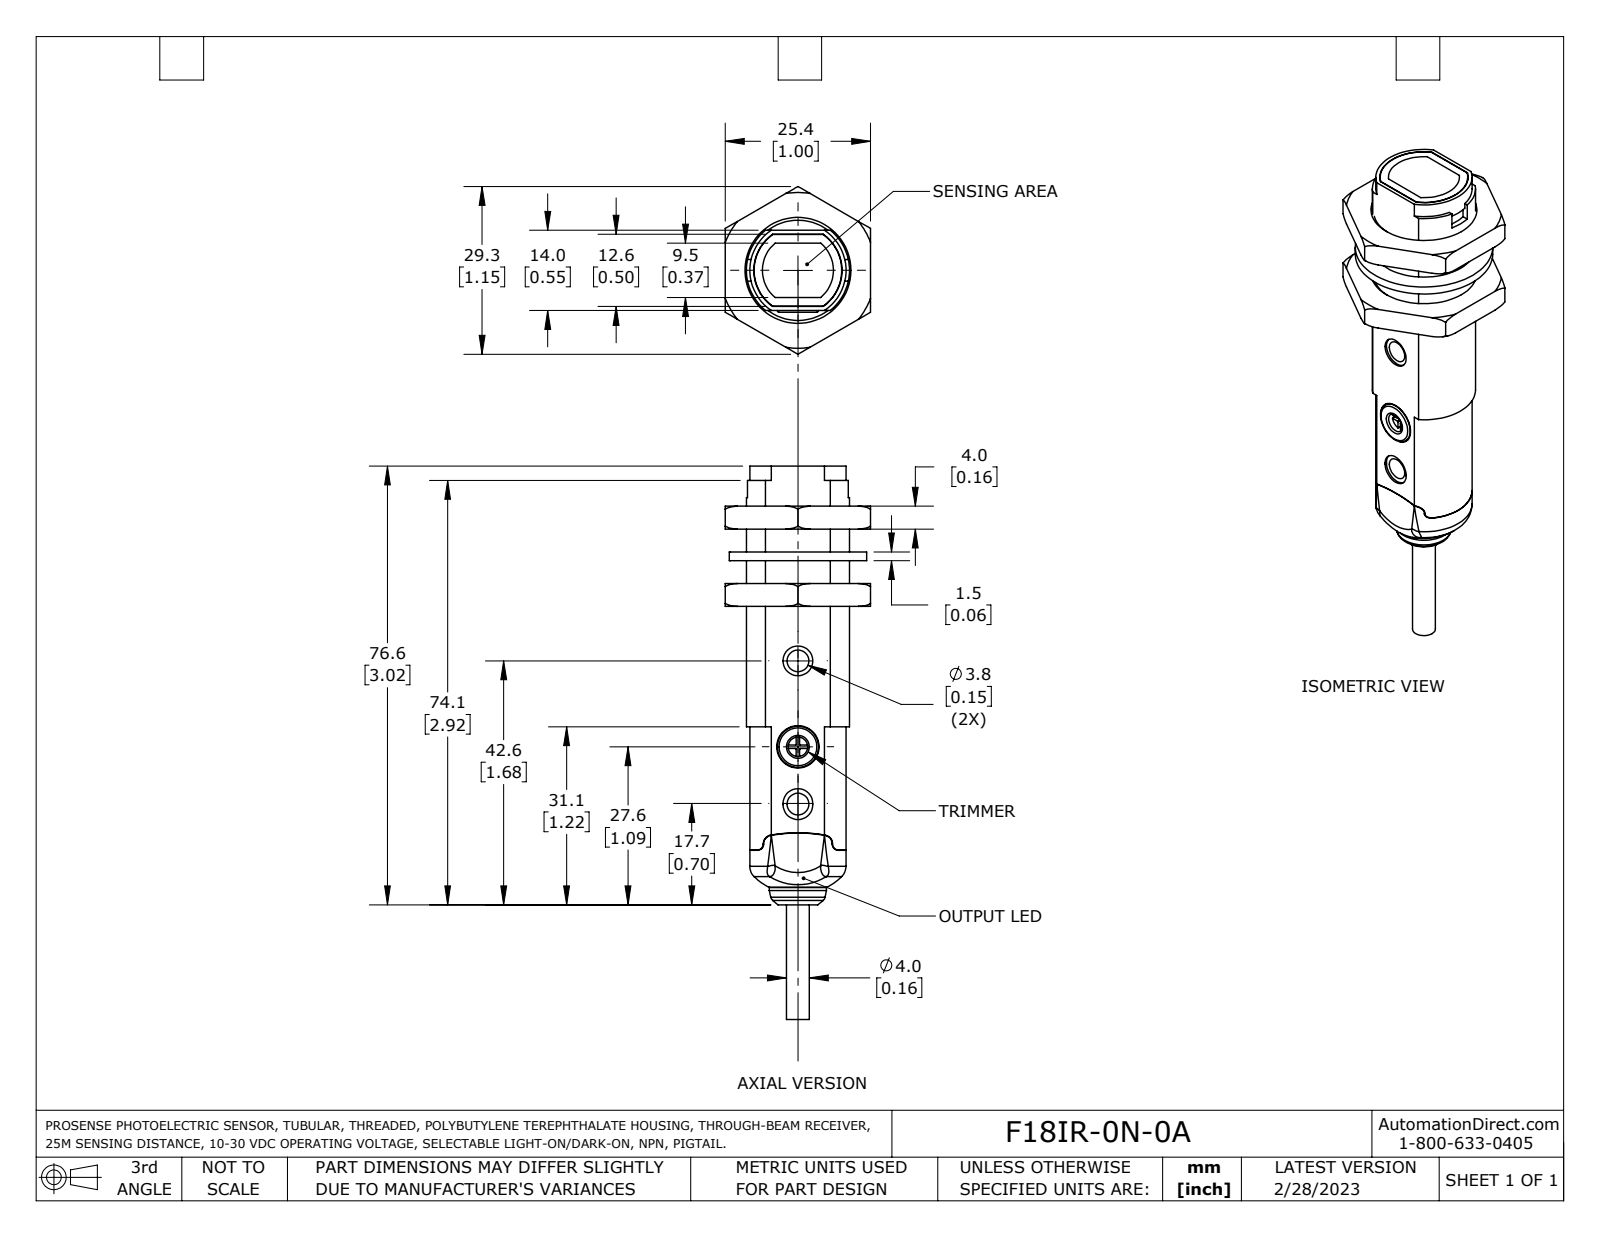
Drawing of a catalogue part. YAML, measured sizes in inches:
part_name: "F18IR-0N-0A"
step_written_by: "SolidWorks 2021 (AUTOMOTIVE_DESIGN)"
units: inches
bodies: {solids: 4, faces: 173, planar: 77, cylindrical: 47, other: 49}
overall_size: [3.802, 1.153, 0.998]
volume: 1.134
surface_area: 12.49
round_holes:
  - {diameter: 0.15, count: 2}
  - {diameter: 0.134, count: 1}
  - {diameter: 0.205, count: 1}
  - {diameter: 0.291, count: 1}
  - {diameter: 0.689, count: 1}
round_bosses_or_shafts:
  - {diameter: 0.945, count: 1}
  - {diameter: 0.709, count: 1}
  - {diameter: 0.394, count: 1}
  - {diameter: 0.283, count: 1}
  - {diameter: 0.157, count: 1}
partial_cylinders:
  - {radius: 0.039, count: 4}
  - {radius: 0.059, count: 4}
  - {radius: 0.102, count: 2}
  - {radius: 1.102, count: 2}
  - {radius: 0.02, count: 1}
  - {radius: 0.301, count: 1}
  - {radius: 0.303, count: 1}
  - {radius: 0.307, count: 1}
face_to_face_distances: [0.157, 0.374, 0.551, 0.531, 0.217, 0.315, 0.998, 0.689, 0.433, 0.059]
hole_center_spacings: [0.394, 0.591, 0.984]
